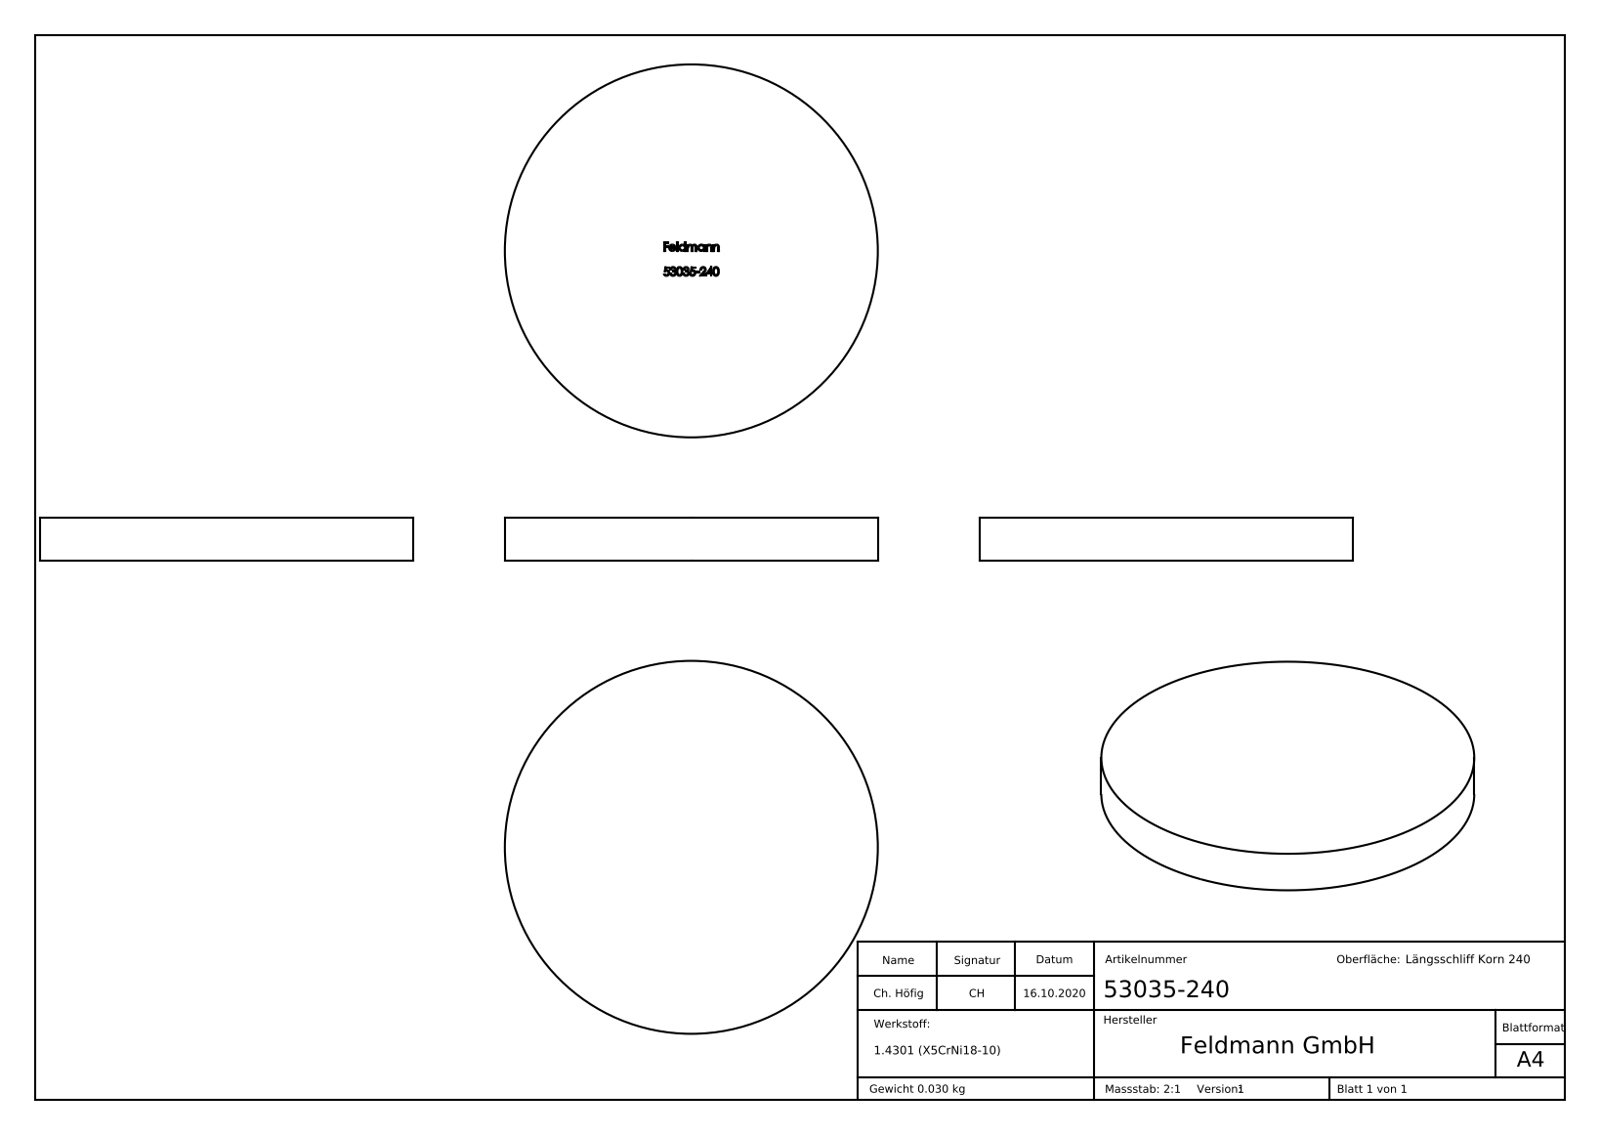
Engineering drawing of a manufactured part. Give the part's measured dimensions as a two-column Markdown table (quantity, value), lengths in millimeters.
| quantity | value |
| --- | --- |
| part name | 53035-240 |
| STEP written by | SolidWorks 2018 (CONFIG_CONTROL_DESIGN) |
| units | millimeters |
| bodies | 1 solid, 238 faces (120 planar, 2 cylindrical, 116 other) |
| overall size | 35 × 35 × 4 |
| volume | 3 848 mm³ |
| surface area | 2 370 mm² |
| round bosses / shafts (diameter × count) | 35 × 1 |
| main face-to-face distances | 4, 3.9, 1.78, 2.45, 0.83, 2.41, 0.79, 0.4, 0.99, 0.71 |
